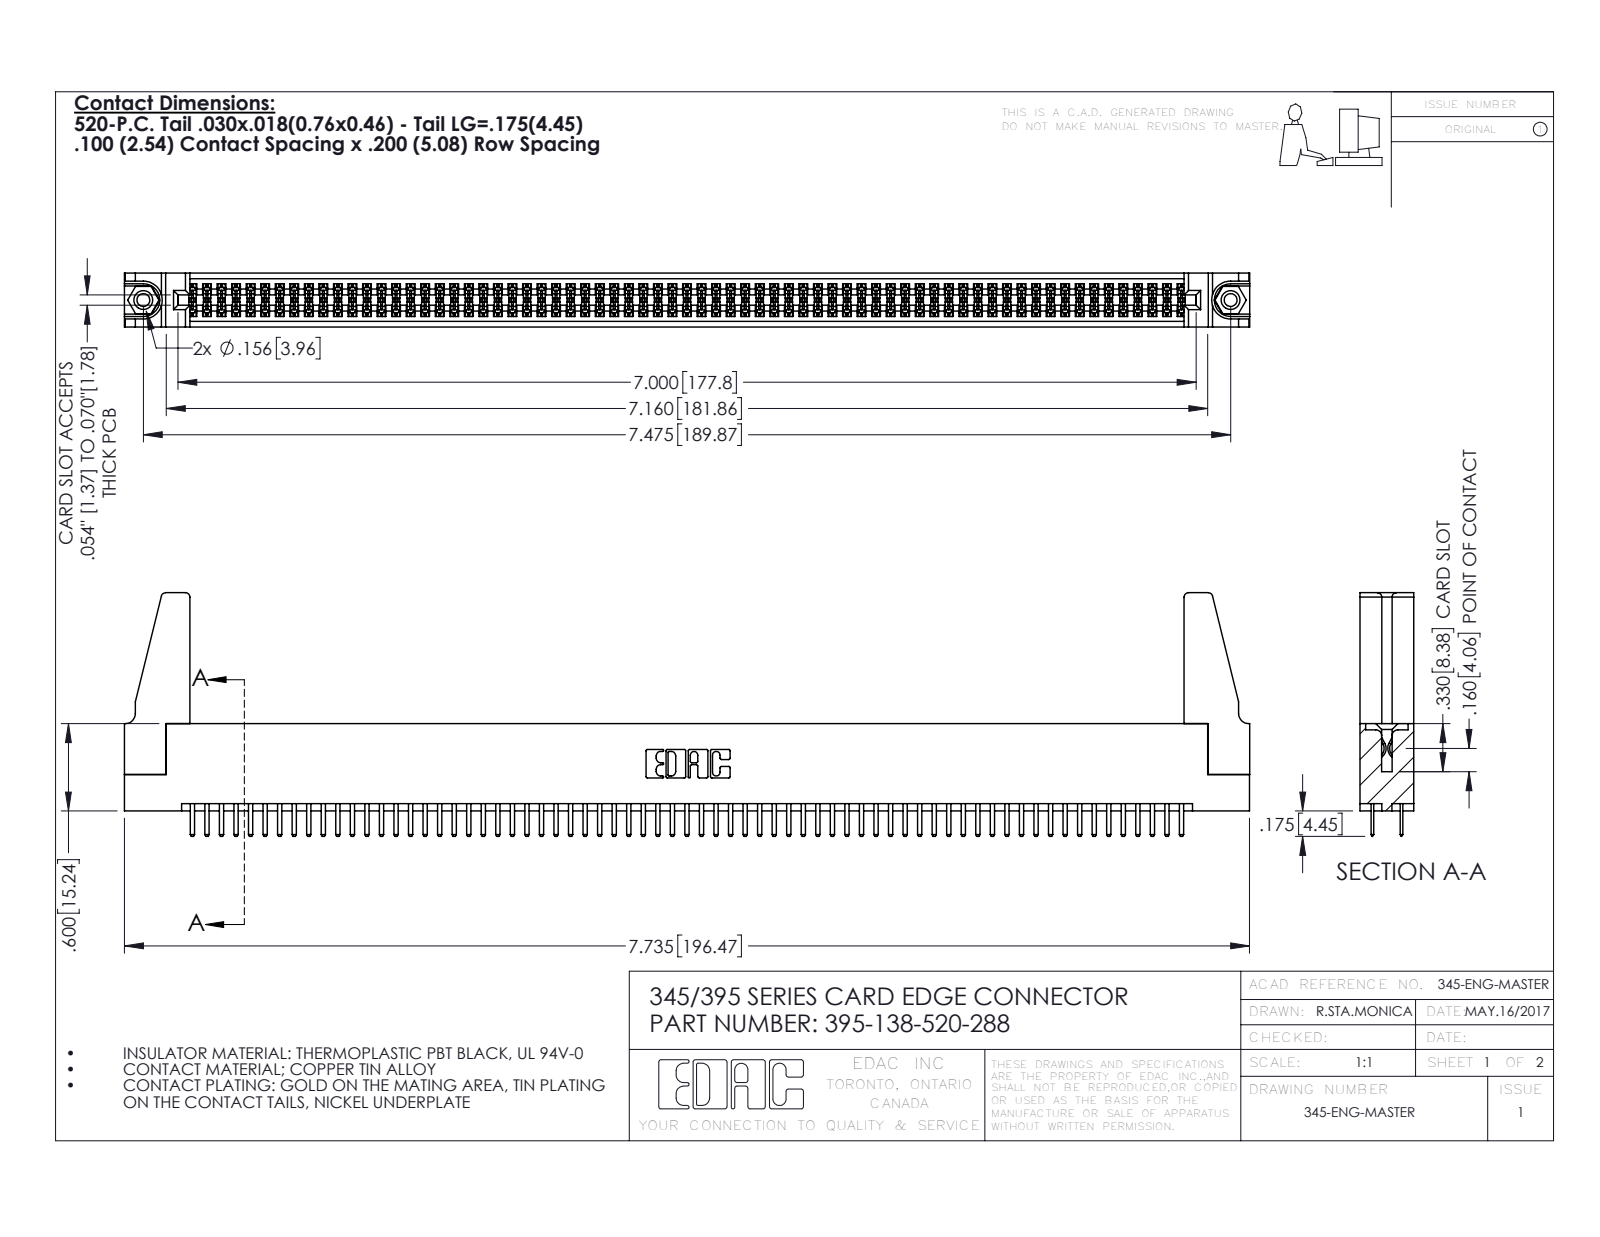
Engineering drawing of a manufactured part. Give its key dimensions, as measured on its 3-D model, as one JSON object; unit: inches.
{"part_name": "395-138-520-288; 345 Part_Flush Mounting Lugs - 0.156 Dia-TH; 345-250-001_345-250-001-102; 345-220-078_345-220-088 (+1 more)", "step_written_by": "SolidWorks 2016 (CONFIG_CONTROL_DESIGN)", "units": "inches", "bodies": {"solids": 143, "faces": 7702, "planar": 4982, "cylindrical": 2704, "other": 16}, "overall_size": [7.736, 1.675, 0.37], "volume_in3": 1.375, "surface_area_in2": 49.62, "round_holes": [[0.089, 2], [0.125, 2], [0.156, 2], [0.064, 1]], "round_bosses_or_shafts": [[0.155, 2]], "partial_cylinders_radius": [[0.006, 207], [0.01, 142], [0.01, 22], [0.03, 8], [0.007, 6], [0.031, 6], [0.026, 3], [0.014, 2]], "face_to_face_distances": [0.072, 0.298, 0.37, 0.2, 0.098, 0.272, 0.025, 0.225, 0.022, 0.072], "hole_center_spacings": [0.27, 7.239, 7.475]}
